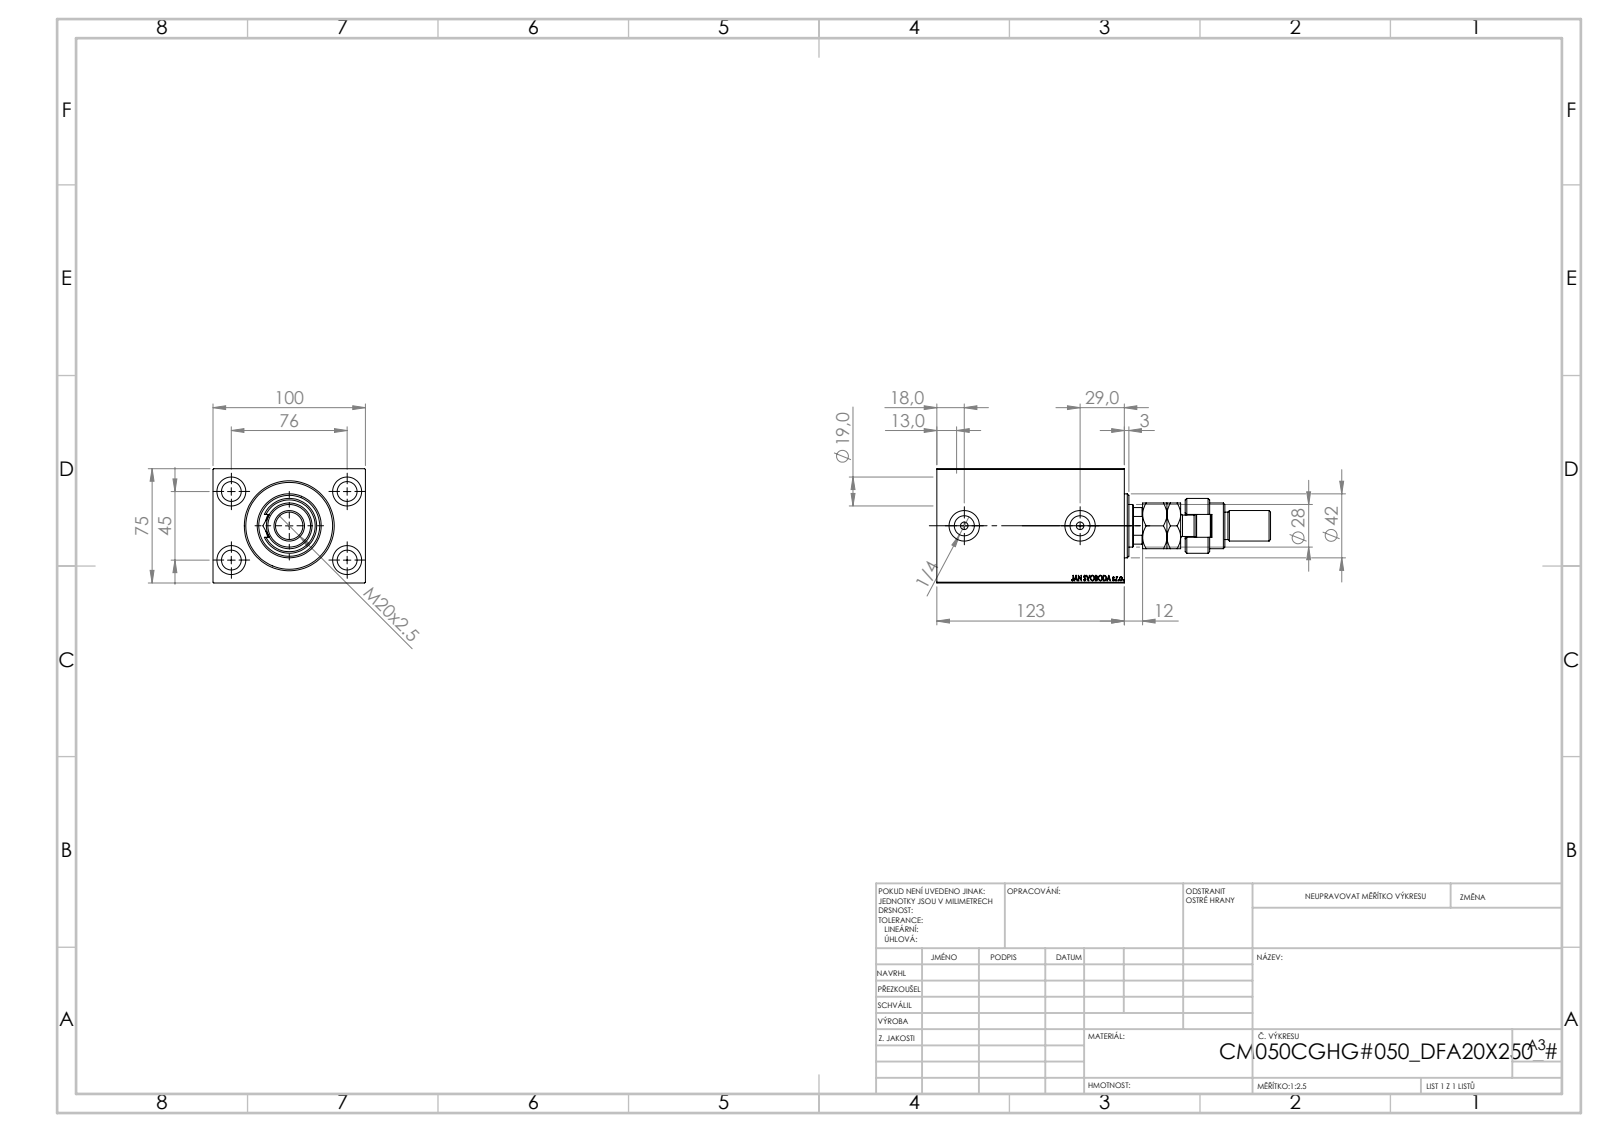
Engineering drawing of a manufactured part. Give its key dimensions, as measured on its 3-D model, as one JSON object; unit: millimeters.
{"part_name": "V450CM_VC_B; MFA; V450CM_C_VCP; V450CM_C_Body (+1 more)", "step_written_by": "SolidWorks 2019 (CONFIG_CONTROL_DESIGN)", "units": "millimeters", "bodies": {"solids": 5, "faces": 950, "planar": 437, "cylindrical": 75, "other": 438}, "overall_size": [219, 100, 75], "volume_mm3": 820420, "surface_area_mm2": 137650, "round_holes": [[13, 4], [19, 4], [5, 2], [13.16, 2], [20, 2], [18.5, 1], [28, 1], [31.5, 1], [50, 1], [52, 1], [57, 1]], "round_bosses_or_shafts": [[42, 1], [36, 1], [30, 1], [22, 1], [20, 1], [18, 1], [14, 1]], "partial_cylinders_radius": [[7.5, 1], [12, 1], [13.5, 1]], "face_to_face_distances": [75, 100, 123, 109, 14, 12, 97, 50, 62, 30], "hole_center_spacings": [44.16, 76, 45, 88.32]}
